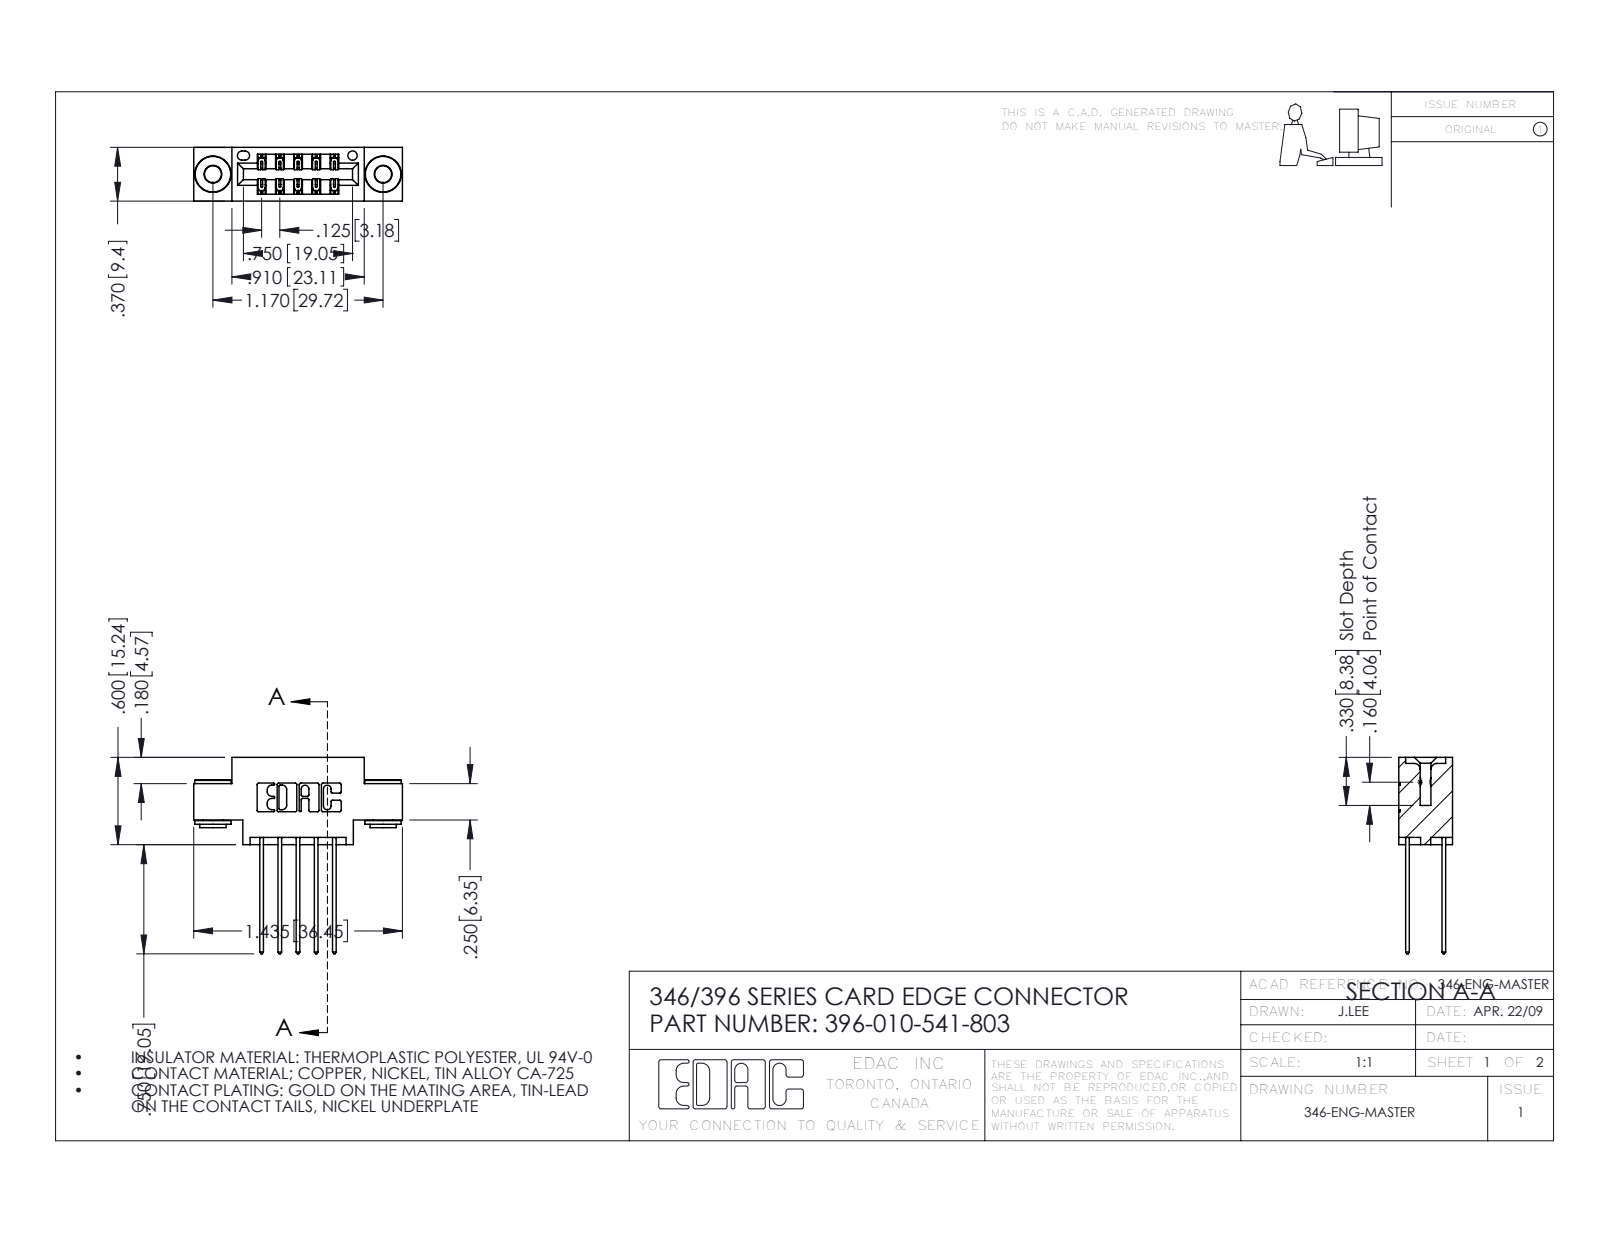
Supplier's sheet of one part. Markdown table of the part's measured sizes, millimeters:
| quantity | value |
| --- | --- |
| part name | 346 Part_0.170 Offset - 0.156 Dia-TH; 345-292-001_345-293-141; 345-250-002_345-250-002-102; 396-010-541-803 |
| STEP written by | SolidWorks 2016 (CONFIG_CONTROL_DESIGN) |
| units | millimeters |
| bodies | 13 solids, 684 faces (440 planar, 236 cylindrical, 8 other) |
| overall size | 36.4 × 34.3 × 9.4 |
| volume | 3 200 mm³ |
| surface area | 4 471 mm² |
| round holes (diameter × count) | 2.9 × 2, 4 × 2, 1.6 × 1 |
| round bosses / shafts (diameter × count) | 6.4 × 2, 4.6 × 2, 3.5 × 2 |
| partial cylindrical surfaces (radius × count) | 0.3 × 22, 0.2 × 15, 0.3 × 10, 0.2 × 6, 0.8 × 6, 0.7 × 3, 0.4 × 2, 0.6 × 2 |
| main face-to-face distances | 6.4, 9.4, 1.2, 8.2, 0.6, 1.8, 7.6, 7, 5.7, 3.8 |
| hole center spacings | 6.2, 24.6, 29.7 |
